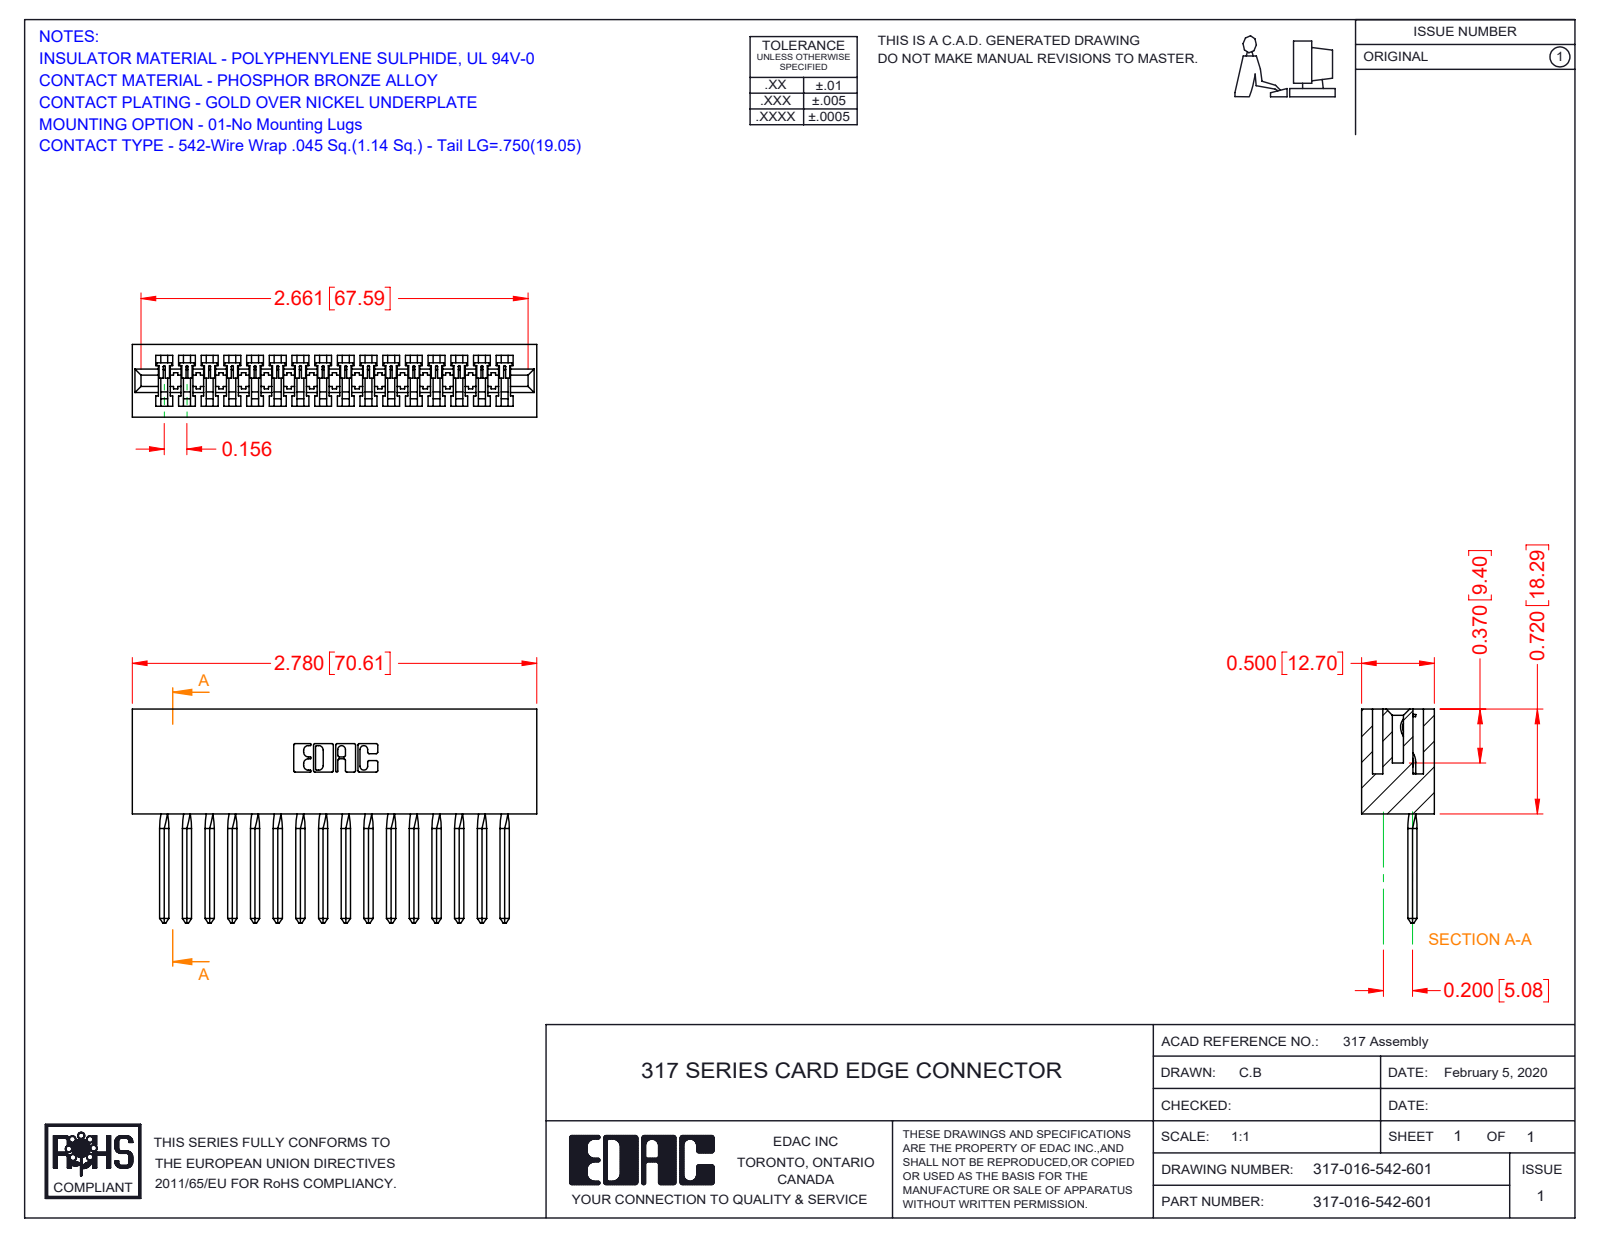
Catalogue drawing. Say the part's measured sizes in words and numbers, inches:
The part is named "317-290-003_542; 317-016-542-601; 317 Part_Lugless". Its 3-D file was written by "SolidWorks 2016 (CONFIG_CONTROL_DESIGN)". It is 17 solids with 1290 faces: 1074 planar, 152 cylindrical and 64 other. Overall it measures 2.78 by 1.47 by 0.5 inches. Its volume is 0.72 cubic inches and its surface area 21.48 square inches. Partial cylindrical surfaces (rounded edges, fillets, slot ends): 32 of radius 0.006, 22 of radius 0.01, 6 of radius 0.007, 6 of radius 0.031, 3 of radius 0.026, 1 of radius 0.074, 1 of radius 0.089, 1 of radius 0.1. The main face-to-face distances are 0.5, 0.075, 0.425, 0.11, 0.35, 0.065, 0.156, 0.22, 0.136, 0.116.
